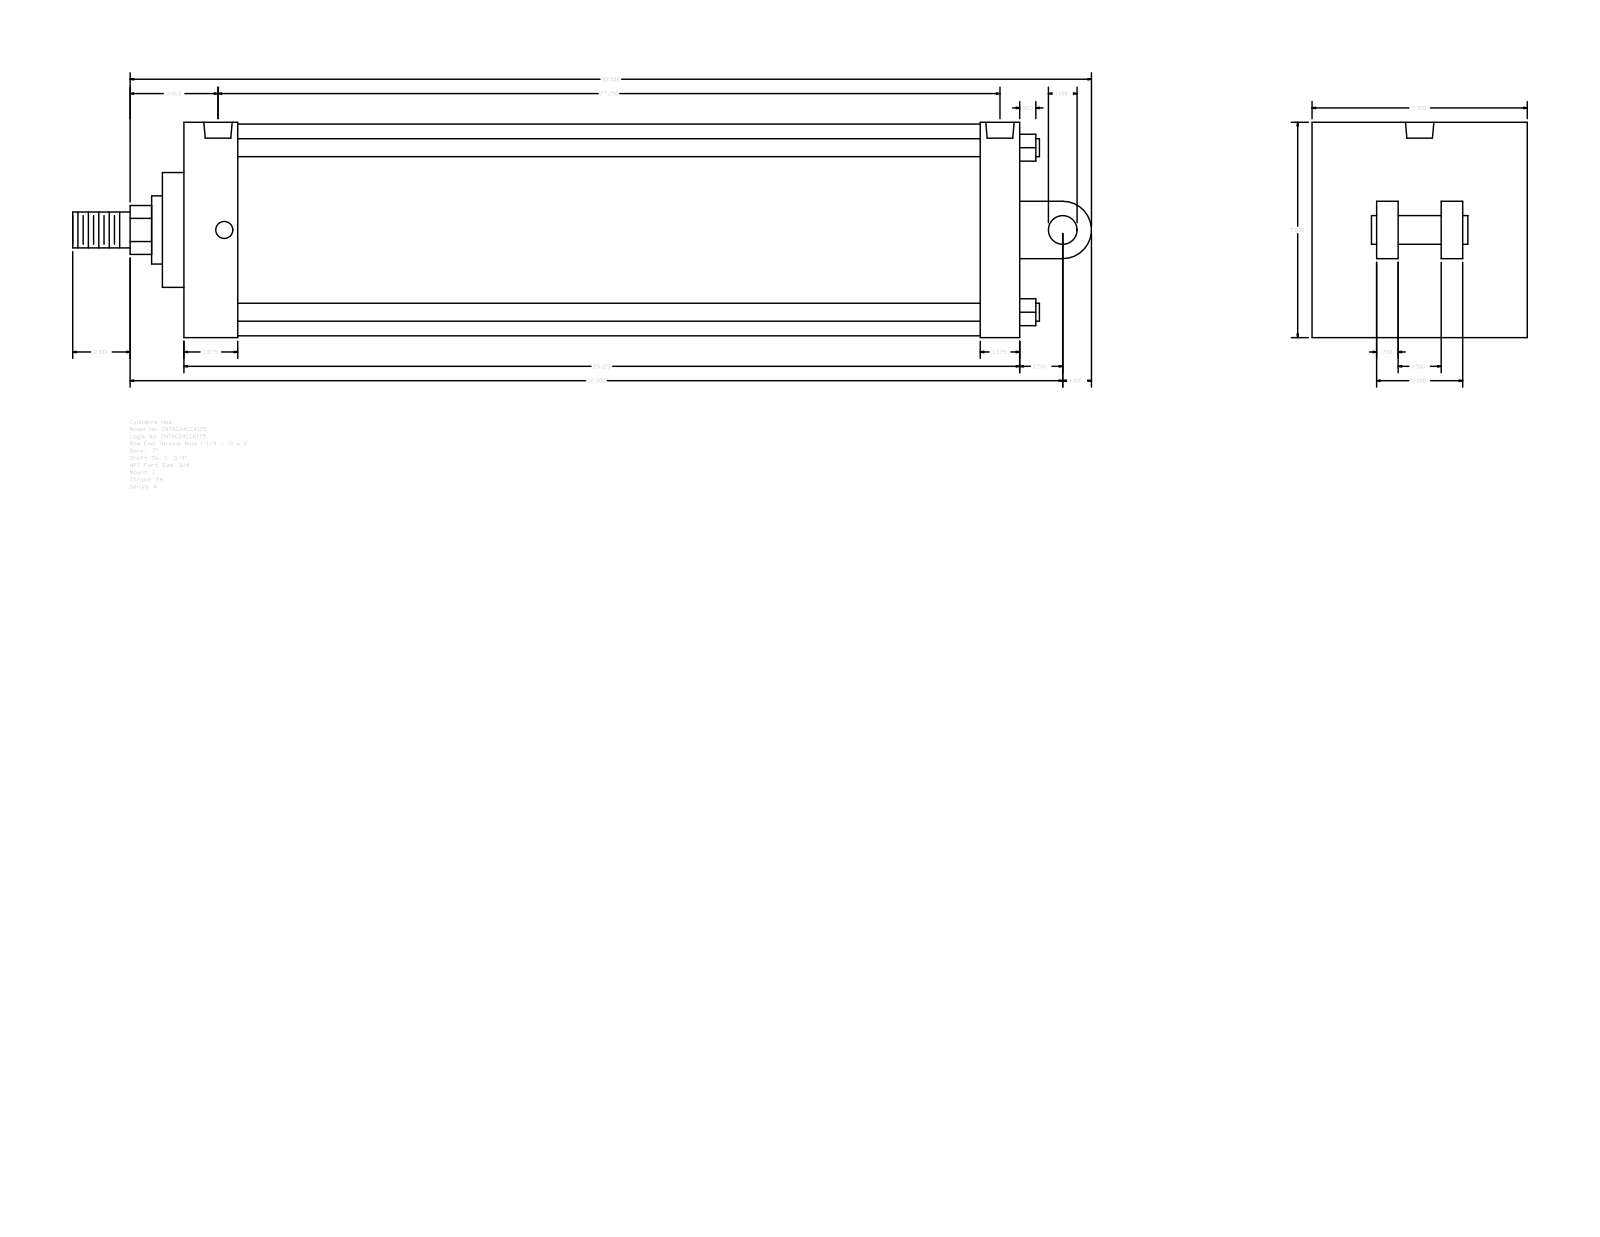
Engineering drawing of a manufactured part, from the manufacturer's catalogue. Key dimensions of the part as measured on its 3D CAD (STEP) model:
Part name (STEP PRODUCT): A_C__0700_1.75
STEP written by: GSSL Pune (CONFIG_CONTROL_DESIGN)
Units: millimetres
Bodies: 0 solids, 104 faces (75 planar, 29 cylindrical, 0 other)
Overall size (bounding box): 901.7 × 190.5 × 190.5
Round holes (diameter × count): ⌀15.08 ×4, ⌀25.12 ×2
Round bosses / shafts (diameter × count): ⌀15.88 ×4, ⌀187.32 ×1, ⌀60.33 ×1, ⌀44.45 ×1, ⌀31.75 ×1, ⌀25.4 ×1
Partial cylindrical surfaces — rounded edges, fillets, slot ends (radius × count): R21.63 ×1, R25.4 ×1
Main face-to-face distances: 190.5, 739.78, 19.05, 76.2, 57.15, 146.05, 44.45, 69.85, 47.63, 692.15
Hole centre spacings: 5.56, 681.03, 686.59, 692.15
